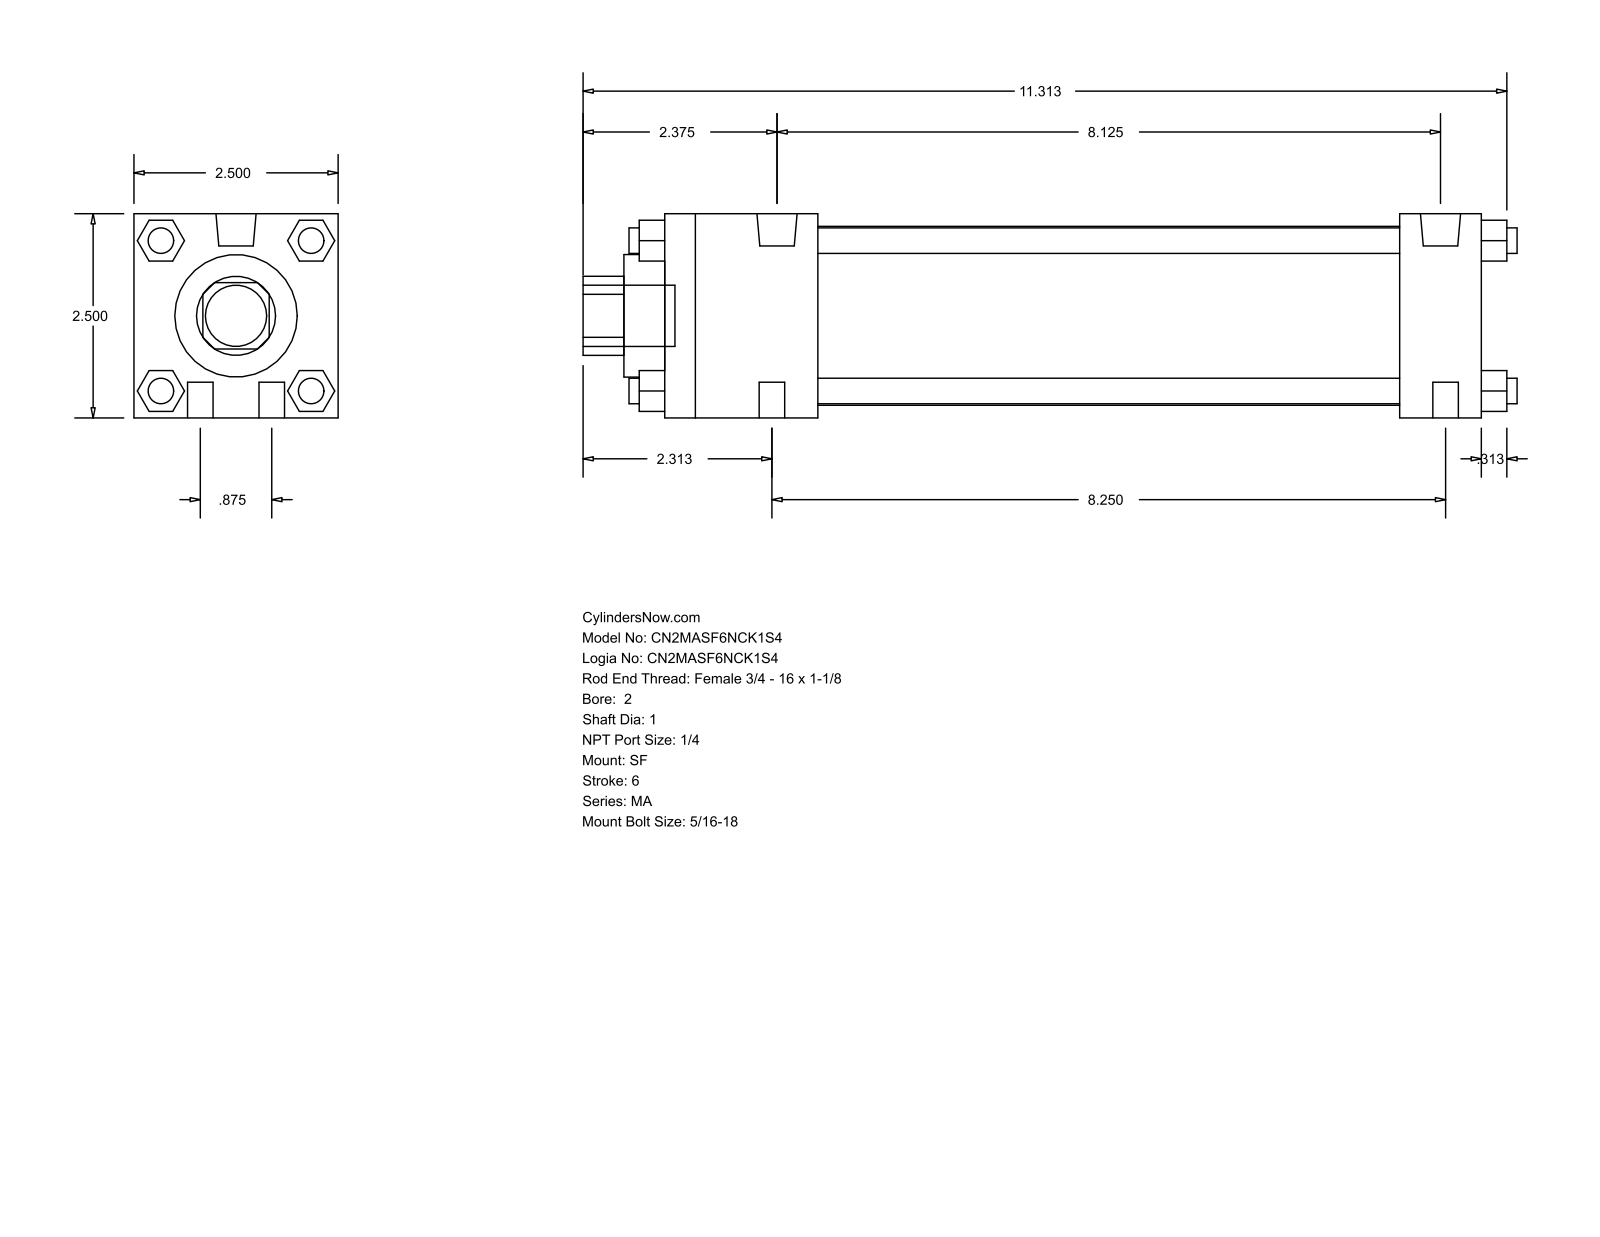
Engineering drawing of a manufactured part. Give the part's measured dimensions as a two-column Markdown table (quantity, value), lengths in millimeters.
| quantity | value |
| --- | --- |
| part name | MA_SF__0200_1 |
| STEP written by | GSSL Pune (CONFIG_CONTROL_DESIGN) |
| units | millimeters |
| bodies | 0 solids, 124 faces (94 planar, 30 cylindrical, 0 other) |
| overall size | 290.51 × 63.5 × 63.5 |
| round holes (diameter × count) | 25.4 × 1, 38.1 × 1, 55.63 × 1 |
| round bosses / shafts (diameter × count) | 7.94 × 10, 12.49 × 2, 19.05 × 1 |
| partial cylindrical surfaces (radius × count) | 12.29 × 1 |
| main face-to-face distances | 63.5, 254, 12.7, 25.4, 228.6, 47.63, 180.97, 206.37, 23.37, 40.47 |
